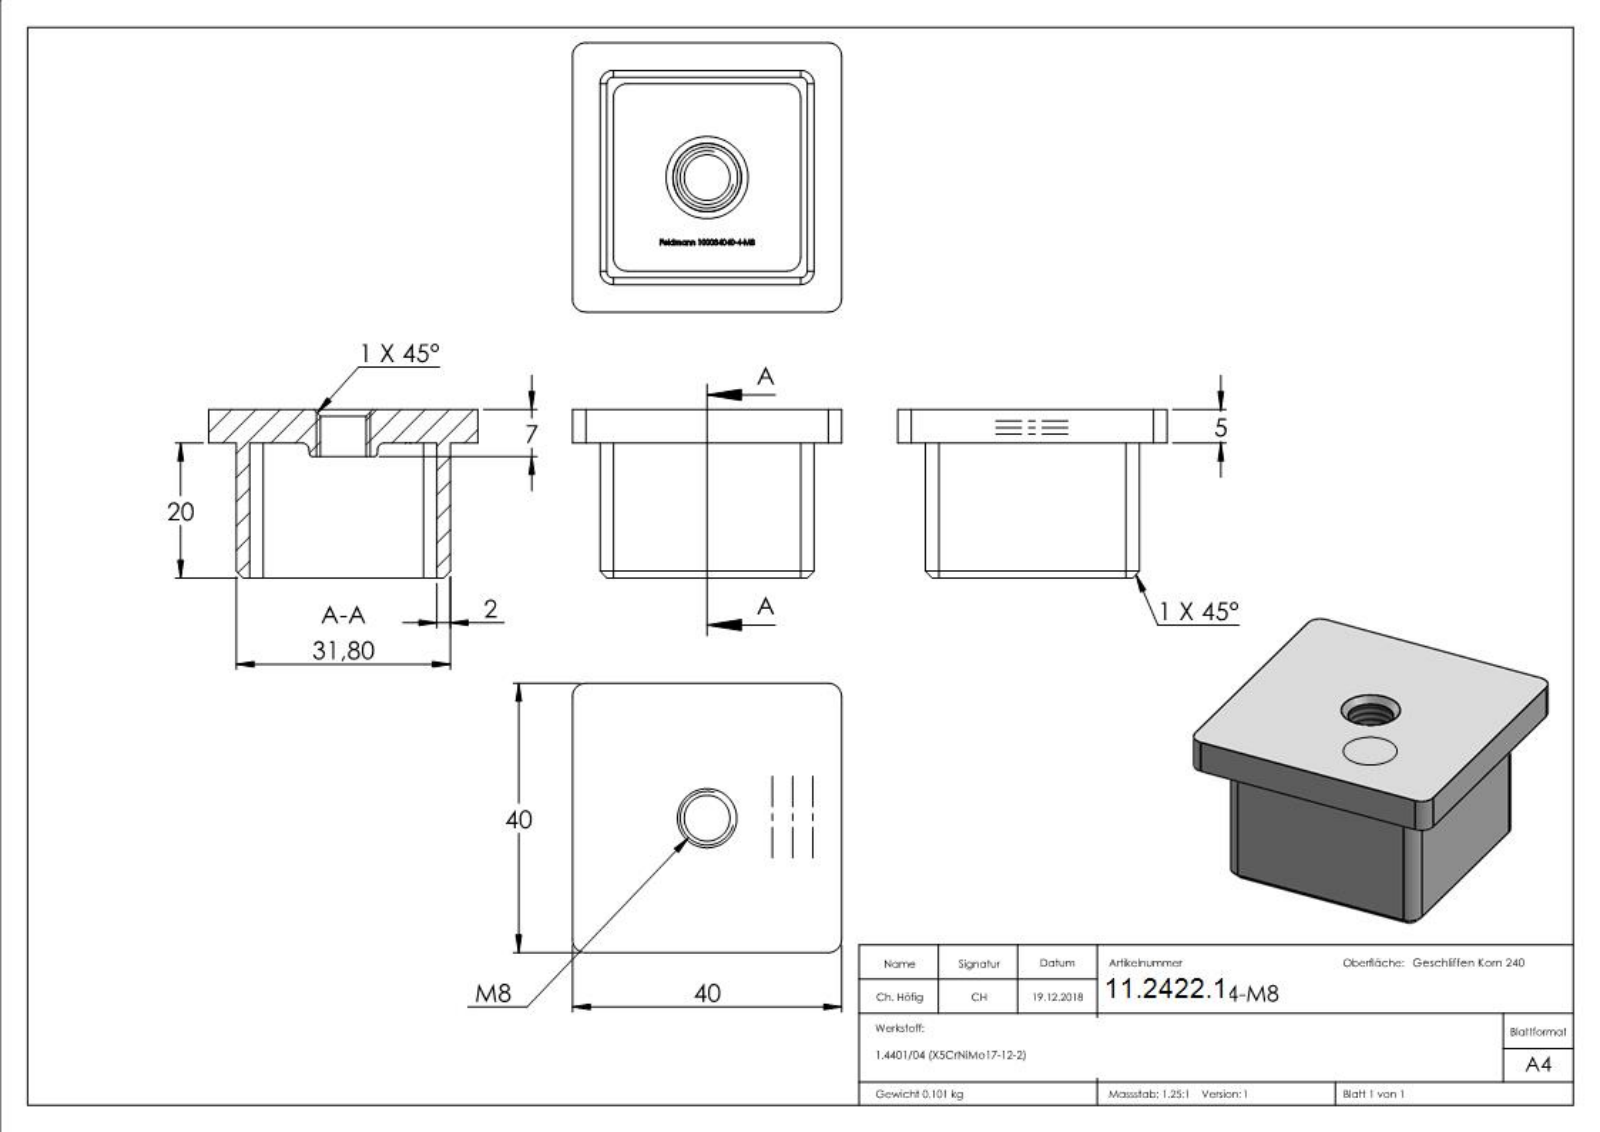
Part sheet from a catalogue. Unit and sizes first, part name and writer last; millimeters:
Units: millimetres
Overall size (bounding box): 40 × 40 × 25
Round holes (diameter × count): ⌀6.8 ×1
Partial cylindrical surfaces — rounded edges, fillets, slot ends (radius × count): R2 ×12
Main face-to-face distances: 2, 29.8, 5, 31.8, 27.8, 4.1, 6.1, 33.9, 35.9, 40
Volume: 12 591 mm³ · Surface area: 8 648 mm²
Bodies: 1 solid, 329 faces (179 planar, 14 cylindrical, 136 other)
Part name (STEP PRODUCT): 100034040-4-M8
STEP written by: SolidWorks 2015 (CONFIG_CONTROL_DESIGN)
